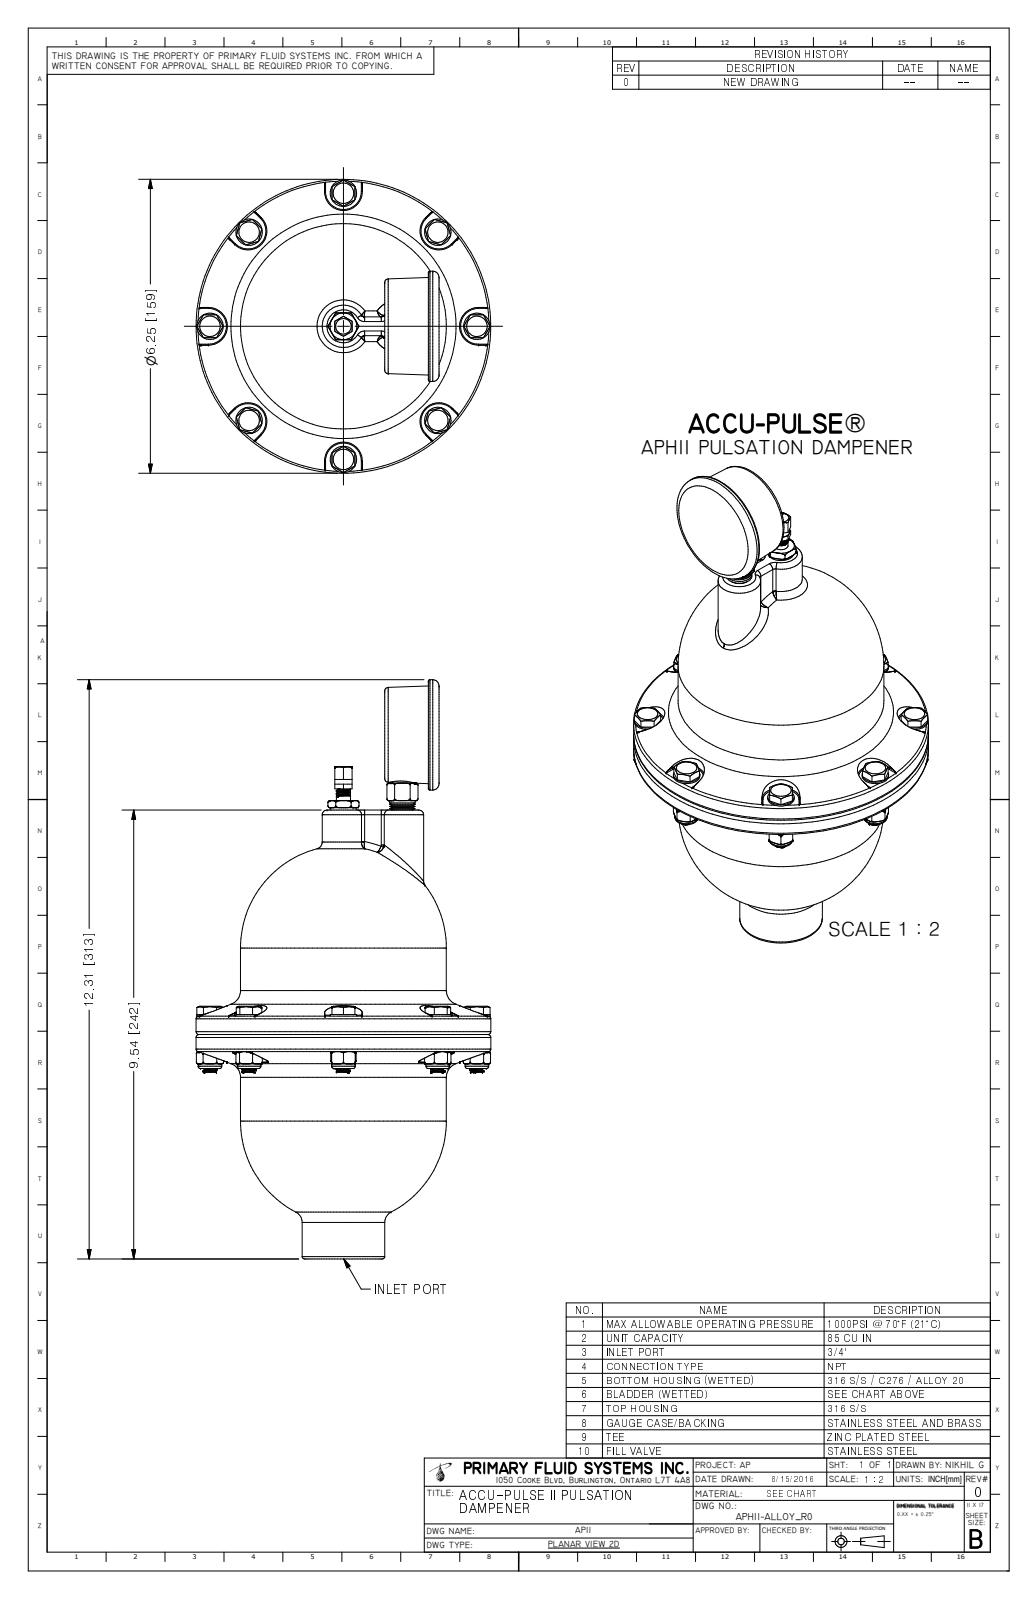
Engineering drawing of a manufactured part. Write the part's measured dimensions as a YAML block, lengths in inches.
part_name: "APHII-ALLOY_R0"
step_written_by: "Autodesk Inventor 2009 (AUTOMOTIVE_DESIGN)"
units: inches
bodies: {solids: 12, faces: 911, planar: 312, cylindrical: 113, other: 486}
overall_size: [12.315, 6.25, 6.25]
volume: 47.13
surface_area: 305.1
round_holes:
  - {diameter: 0.437, count: 1}
  - {diameter: 3.865, count: 1}
round_bosses_or_shafts:
  - {diameter: 0.216, count: 9}
  - {diameter: 0.56, count: 8}
  - {diameter: 0.5, count: 8}
  - {diameter: 0.9, count: 2}
  - {diameter: 0.54, count: 2}
  - {diameter: 6.25, count: 1}
  - {diameter: 4.365, count: 1}
  - {diameter: 4.365, count: 1}
partial_cylinders:
  - {radius: 0.02, count: 32}
  - {radius: 0.1, count: 18}
  - {radius: 0.4, count: 8}
  - {radius: 0.075, count: 4}
face_to_face_distances: [0.126, 0.013, 0.113, 1.15, 1.137, 1.024, 0.493, 0.5, 0.11, 4.715]
hole_center_spacings: [1.25]
